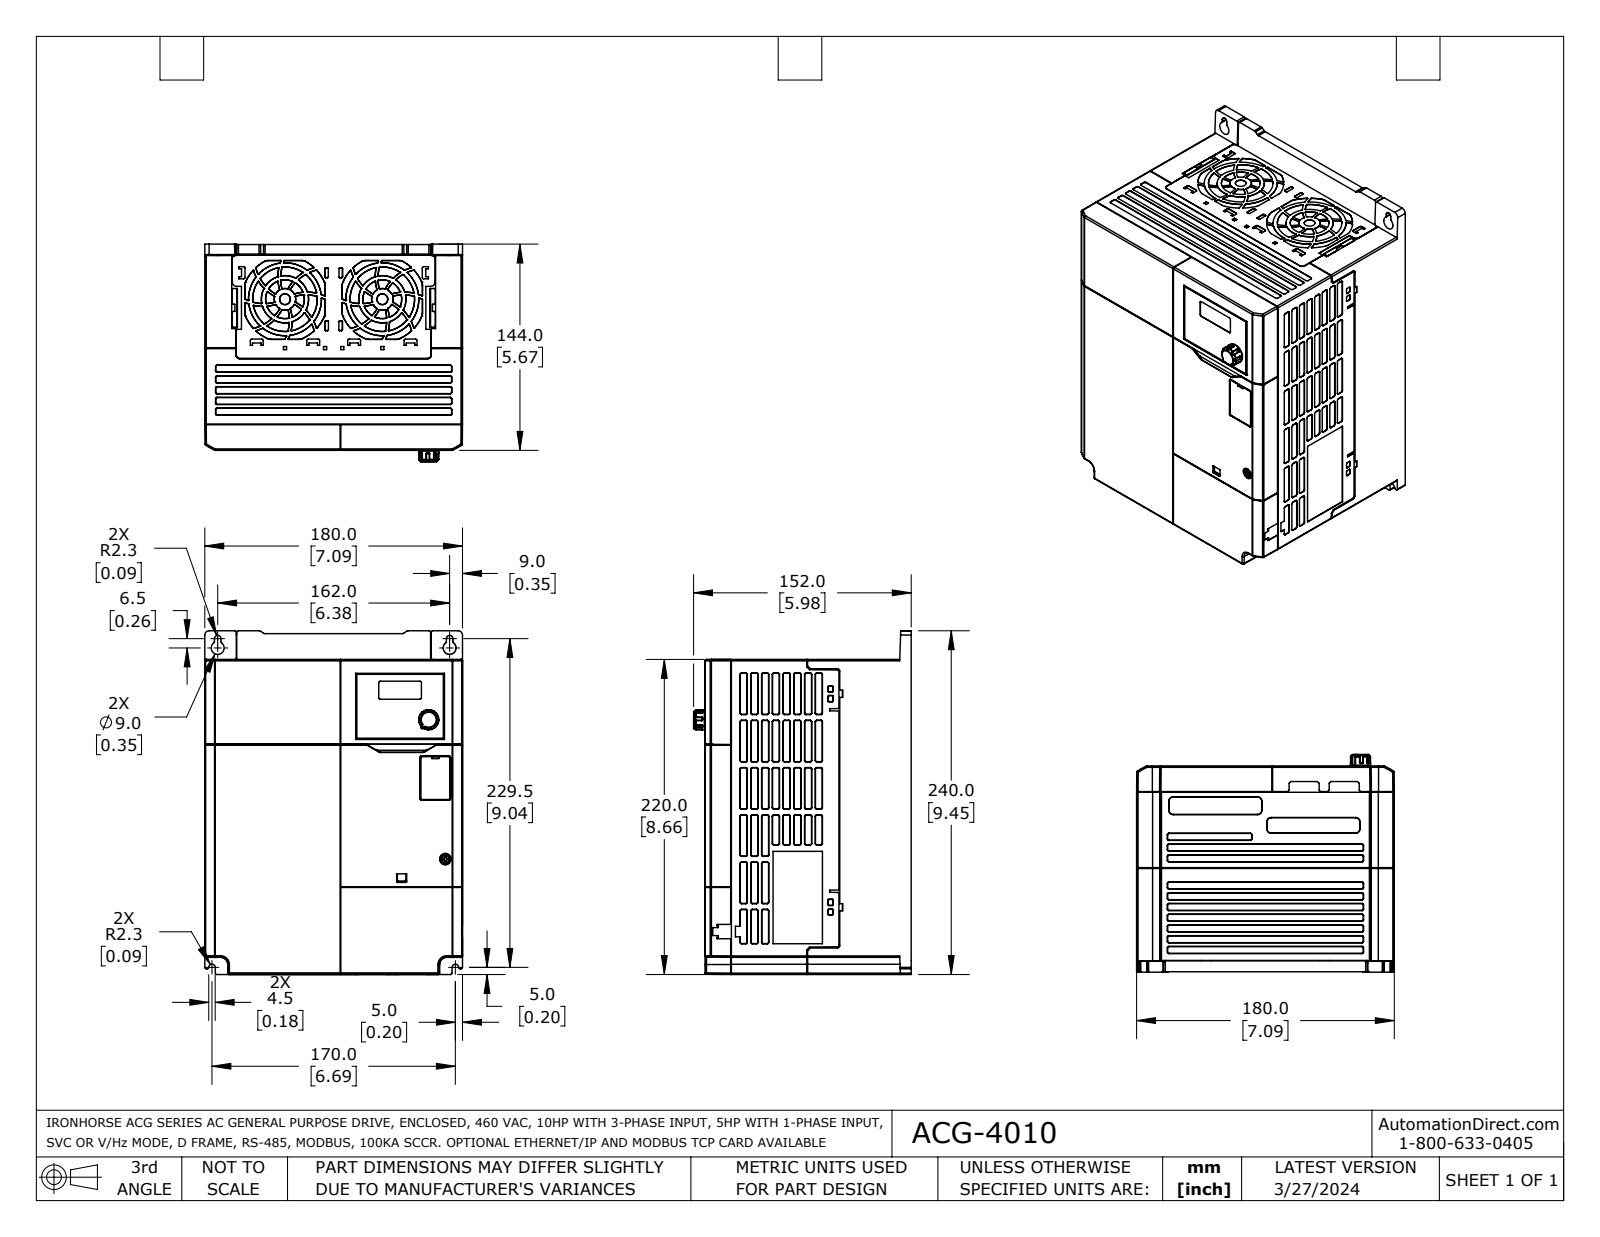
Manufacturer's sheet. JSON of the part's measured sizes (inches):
{"part_name": "ACG-4010", "step_written_by": "SolidWorks 2021 (AUTOMOTIVE_DESIGN)", "units": "inches", "bodies": {"solids": 3, "faces": 5218, "planar": 2417, "cylindrical": 929, "other": 1872}, "overall_size": [9.449, 7.087, 5.984], "volume_in3": 87.68, "surface_area_in2": 753.3, "round_holes": [[0.039, 1], [0.276, 1], [0.417, 1], [0.472, 1]], "round_bosses_or_shafts": [[0.551, 1], [0.543, 1], [0.236, 1]], "partial_cylinders_radius": [[0.02, 587], [0.039, 88], [0.008, 65], [0.012, 27], [0.024, 16], [0.047, 10], [0.079, 5], [0.059, 4]], "face_to_face_distances": [5.316, 0.165, 5.48, 0.134, 5.346, 0.031, 0.039, 7.047, 0.126, 5.354], "hole_center_spacings": [0.276, 2.155, 2.191, 3.675, 3.858, 5.693]}
